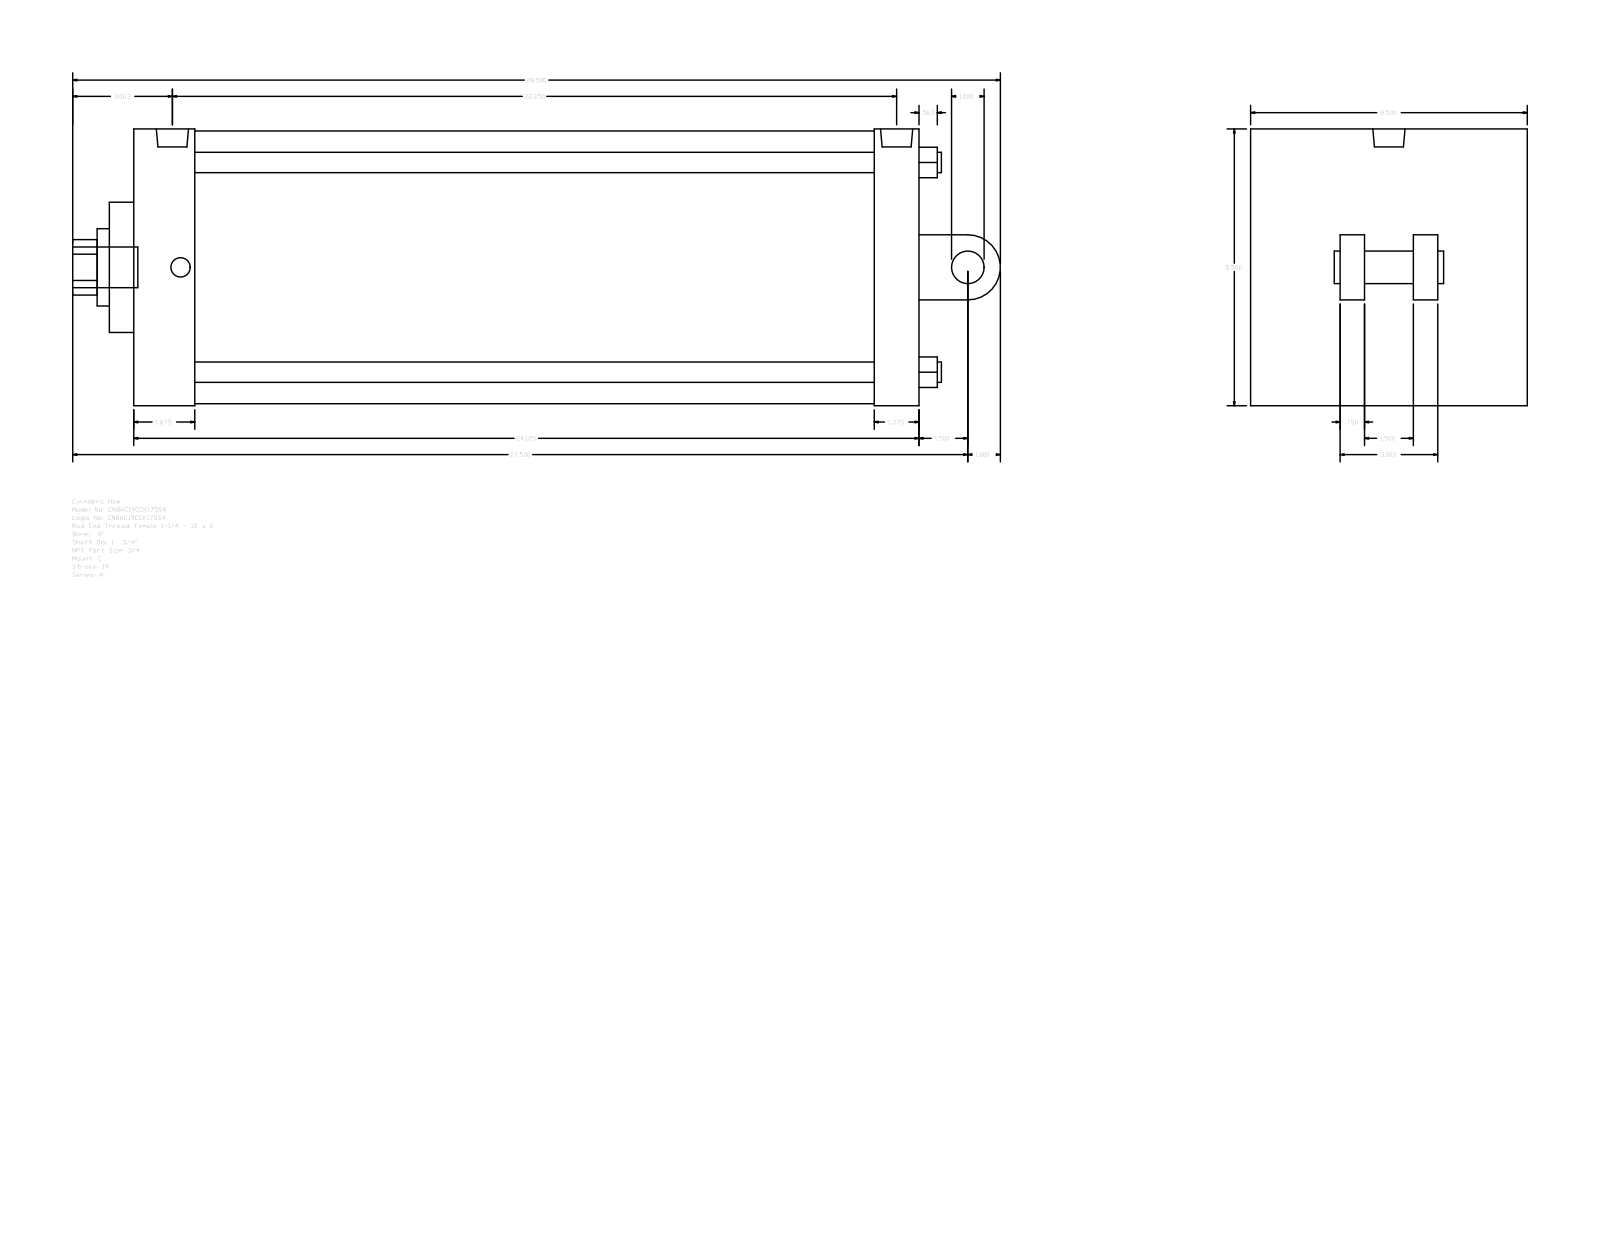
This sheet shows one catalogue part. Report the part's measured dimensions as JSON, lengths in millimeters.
{"part_name": "A_C__0800_1.75", "step_written_by": "GSSL Pune (CONFIG_CONTROL_DESIGN)", "units": "millimeters", "bodies": {"solids": 0, "faces": 104, "planar": 75, "cylindrical": 29, "other": 0}, "overall_size": [723.9, 215.9, 215.9], "round_holes": [[15.88, 4], [15.08, 2], [25.12, 1], [44.45, 1], [60.33, 1], [212.72, 1]], "round_bosses_or_shafts": [[15.08, 2], [31.75, 1], [25.4, 1], [25.12, 1]], "partial_cylinders_radius": [[21.63, 1], [25.4, 1]], "face_to_face_distances": [612.78, 215.9, 19.05, 57.15, 34.92, 47.63, 565.15, 577.86, 530.23, 88.9], "hole_center_spacings": [115.67, 163.58, 231.34, 6.35]}
